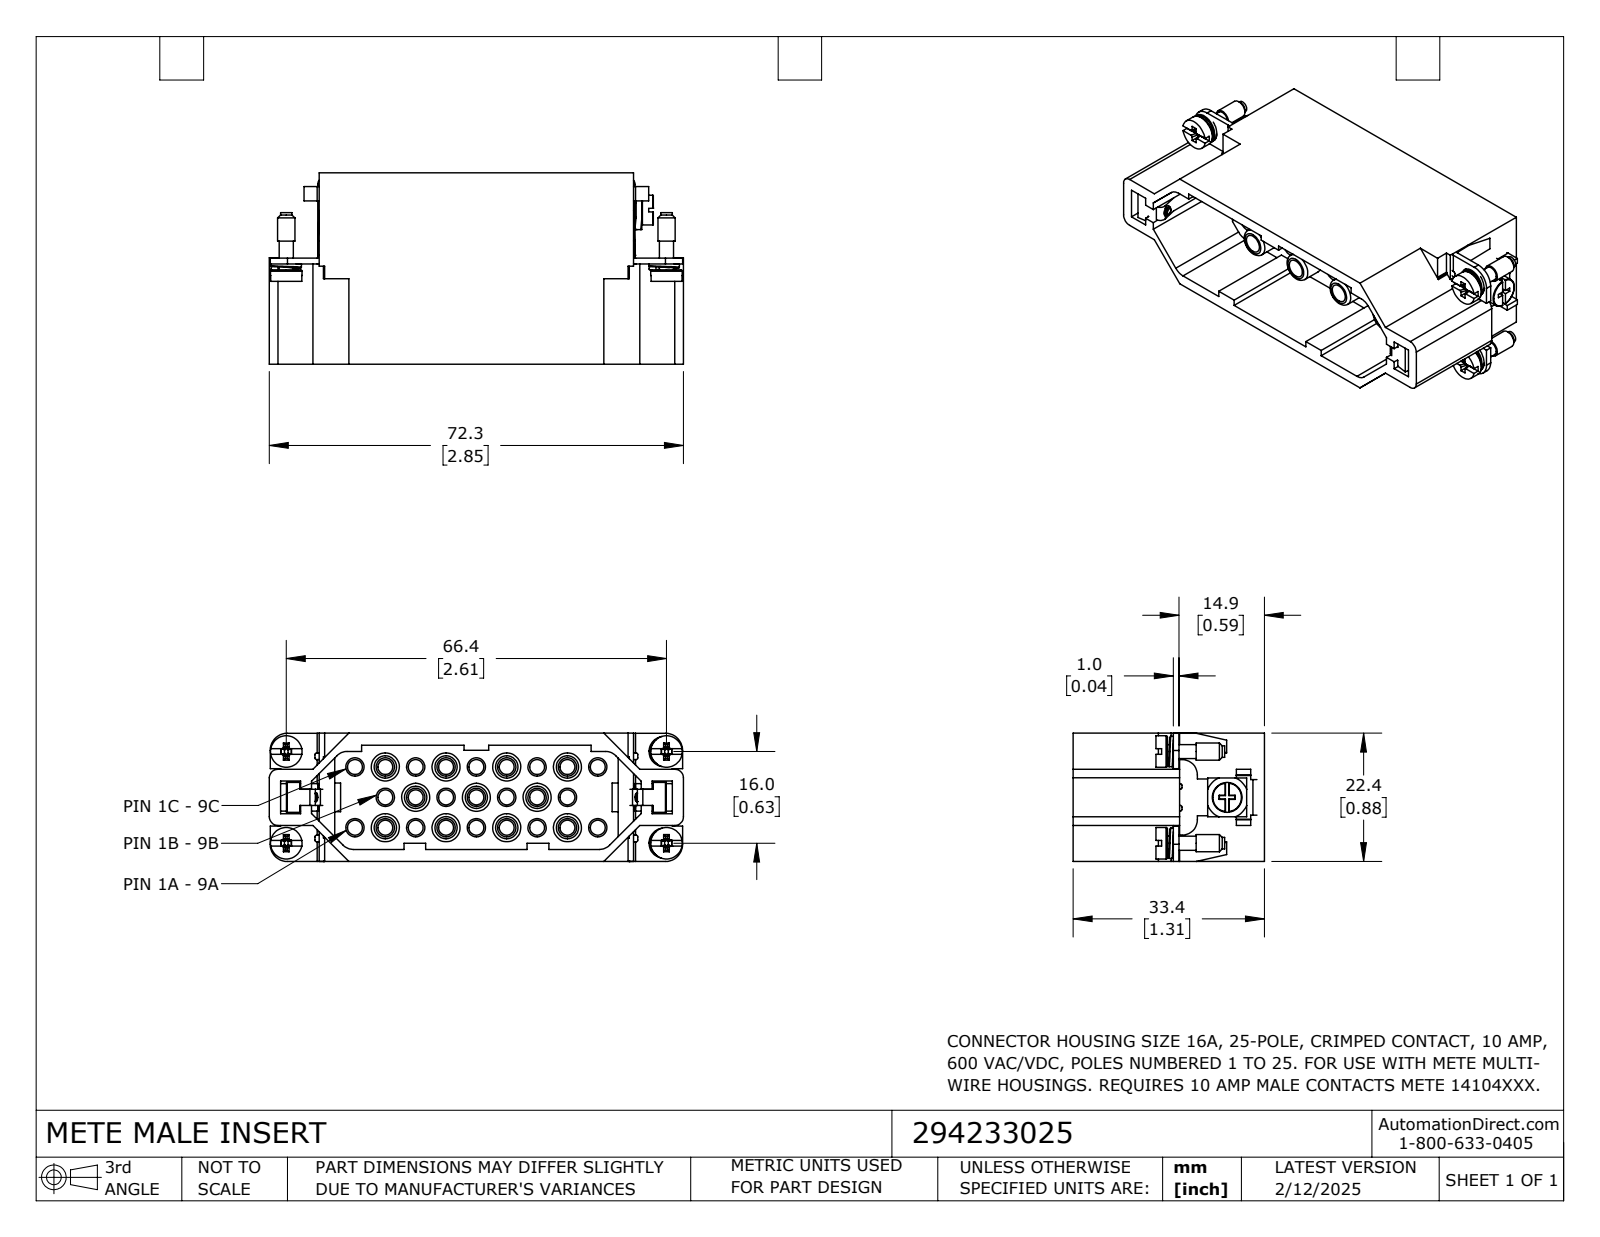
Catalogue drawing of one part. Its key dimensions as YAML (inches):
part_name: "294233025"
step_written_by: "SolidWorks 2024 (CONFIG_CONTROL_DESIGN)"
units: inches
bodies: {solids: 13, faces: 909, planar: 476, cylindrical: 350, other: 83}
overall_size: [2.846, 1.315, 0.882]
volume: 1.726
surface_area: 26.36
round_holes:
  - {diameter: 0.102, count: 25}
  - {diameter: 0.126, count: 25}
  - {diameter: 0.098, count: 5}
  - {diameter: 0.114, count: 4}
  - {diameter: 0.118, count: 1}
round_bosses_or_shafts:
  - {diameter: 0.193, count: 11}
  - {diameter: 0.217, count: 4}
  - {diameter: 0.209, count: 4}
  - {diameter: 0.118, count: 4}
  - {diameter: 0.096, count: 4}
  - {diameter: 0.079, count: 4}
  - {diameter: 0.059, count: 2}
  - {diameter: 0.205, count: 1}
partial_cylinders:
  - {radius: 0.01, count: 32}
  - {radius: 0.004, count: 13}
  - {radius: 0.043, count: 13}
  - {radius: 0.012, count: 12}
  - {radius: 0.098, count: 6}
  - {radius: 0.059, count: 4}
  - {radius: 0.118, count: 4}
  - {radius: 0.106, count: 2}
face_to_face_distances: [0.882, 0.083, 0.799, 0.039, 0.248, 0.717, 0.705, 0.551, 0.165, 0.051]
hole_center_spacings: [0.467, 0.209, 0.295, 0.417, 0.66, 0.626, 0.86, 0.59]
